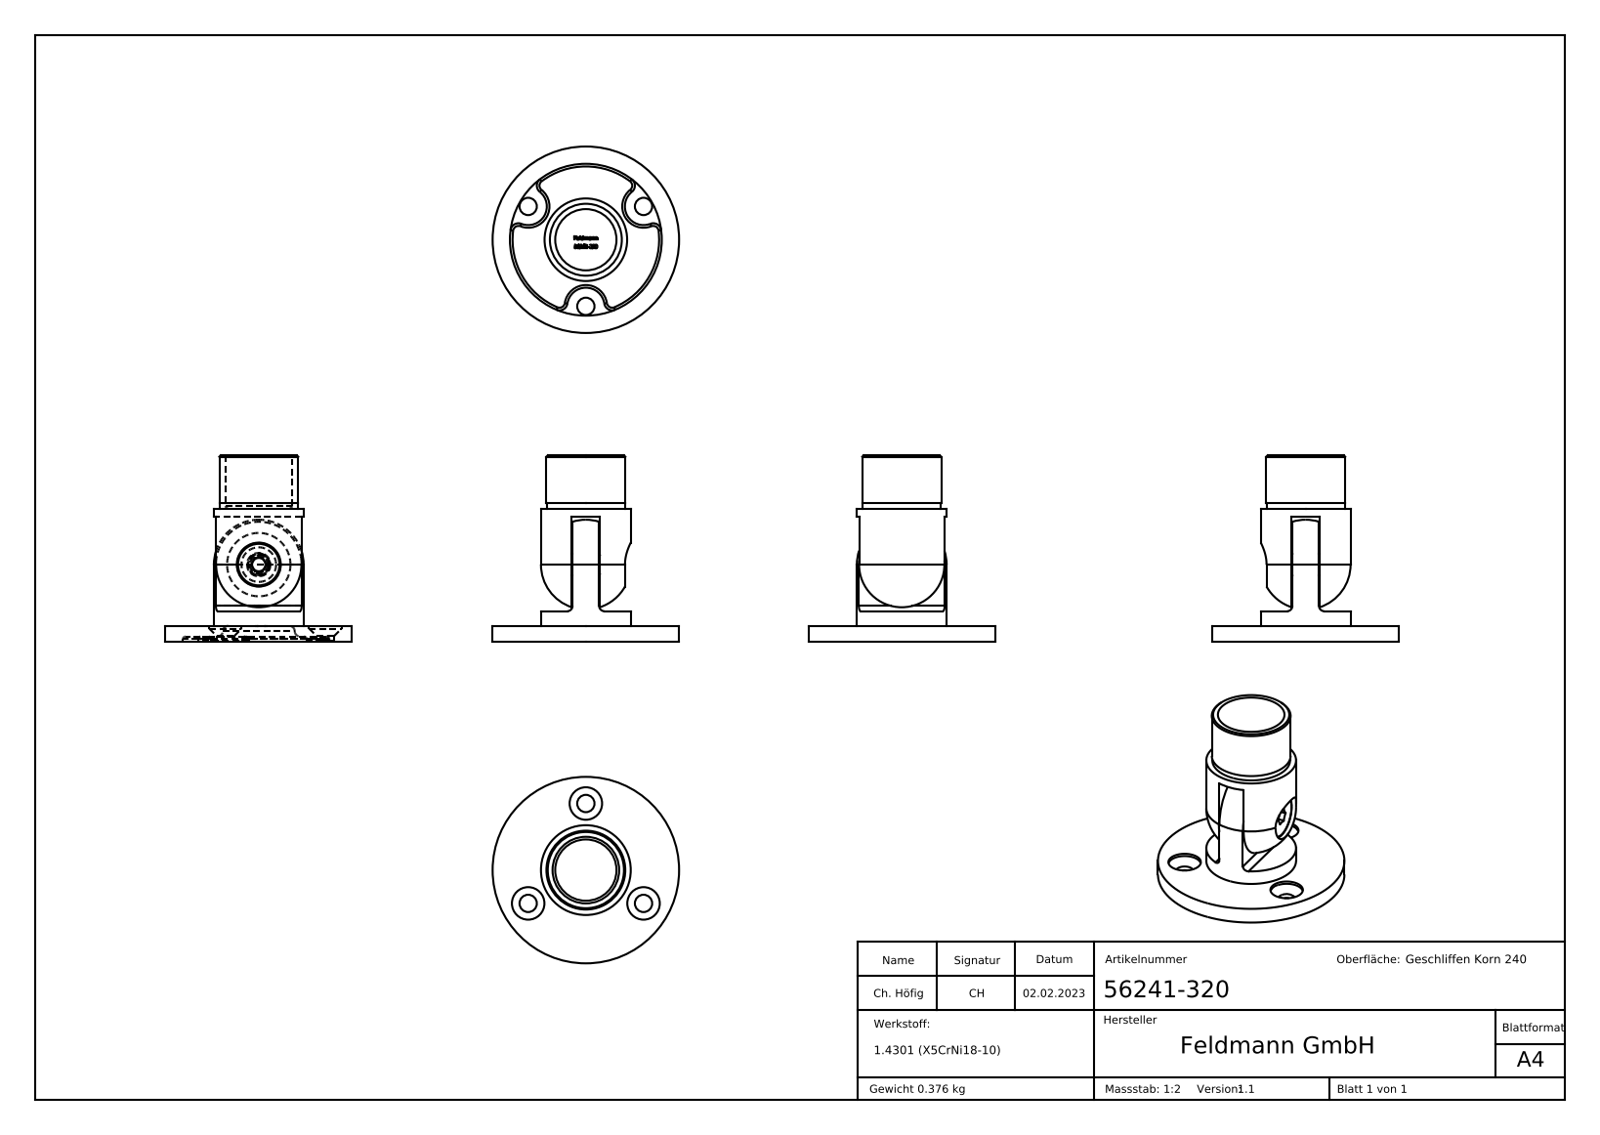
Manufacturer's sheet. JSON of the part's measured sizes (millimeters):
{"part_name": "56241-320; 5624X-320 Teil2_56241-320 Teil2; 5624X-320 Teil1_56241-320 Teil1; socket countersunk head screw_din_DIN 7991 - M8 x 20 --- 20S", "step_written_by": "SolidWorks 2018 (CONFIG_CONTROL_DESIGN)", "units": "millimeters", "bodies": {"solids": 3, "faces": 352, "planar": 157, "cylindrical": 41, "other": 154}, "overall_size": [70, 70, 70], "volume_mm3": 48566, "surface_area_mm2": 24239, "round_holes": [[6.5, 3], [12.2, 3], [6.8, 1], [8.2, 1], [16.5, 1], [25, 1], [57, 1]], "round_bosses_or_shafts": [[70, 1], [33.7, 1], [29.6, 1], [29.2, 1], [15.57, 1], [13, 1], [8, 1]], "partial_cylinders_radius": [[3, 6], [7, 3], [2, 2]], "face_to_face_distances": [6, 2, 4, 10.25, 10, 5.5, 50, 48, 44, 10.5], "hole_center_spacings": [25, 43.3]}
